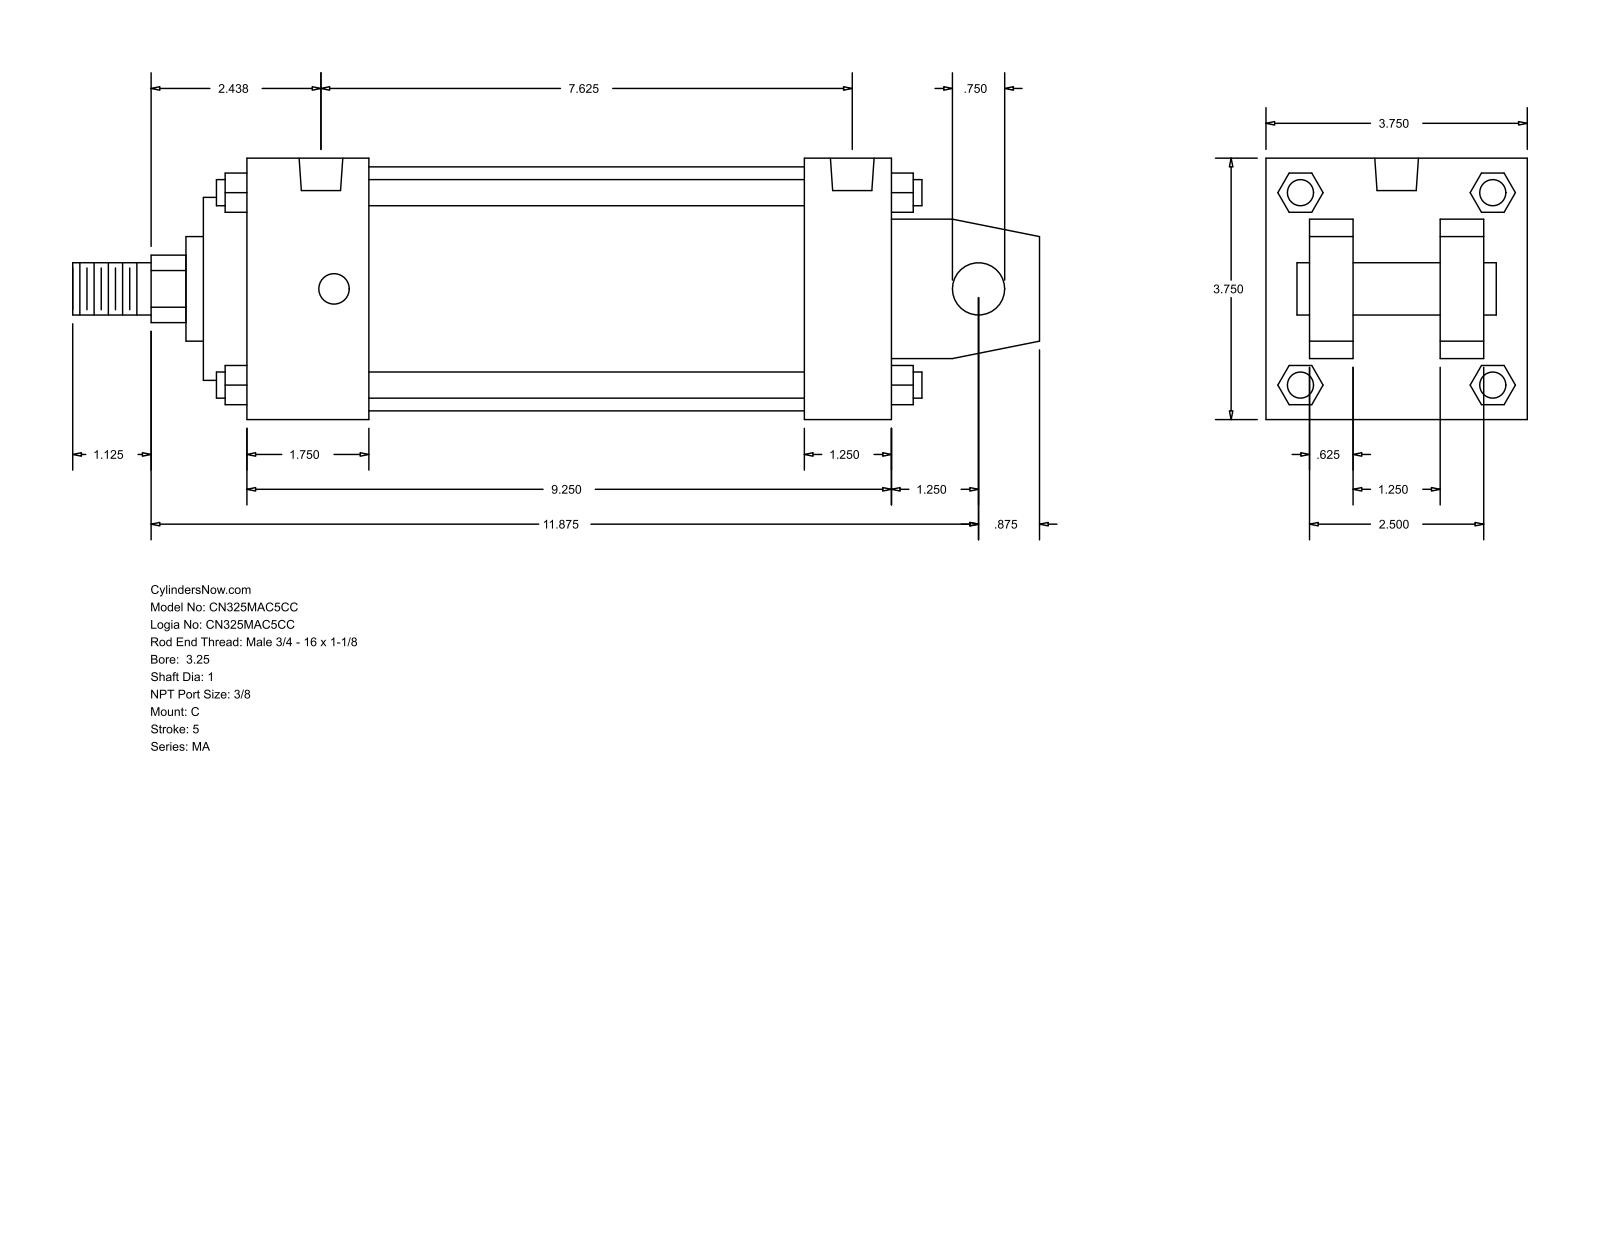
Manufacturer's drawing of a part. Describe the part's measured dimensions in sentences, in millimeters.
The part is named "MA_C__0325_1". Its 3-D file was written by "GSSL Pune (CONFIG_CONTROL_DESIGN)". It is 0 solids with 141 faces: 109 planar, 32 cylindrical and 0 other. Overall it measures 352.43 by 95.25 by 95.25 millimeters. Round holes: 4 of diameter 11.11, 2 of diameter 15.93. Round bosses or shafts: 4 of diameter 9.53, 2 of diameter 19.05, 1 of diameter 88.9, 1 of diameter 66.67, 1 of diameter 38.1, 1 of diameter 25.4. Partial cylindrical surfaces (rounded edges, fillets, slot ends): 1 of radius 12.29. The main face-to-face distances are 95.24, 15.87, 63.5, 234.96, 31.76, 31.74, 79.37, 47.63, 203.2, 44.46. The hole center spacings are 184.15, 4.76, 4.77, 188.91, 188.92, 193.68.
